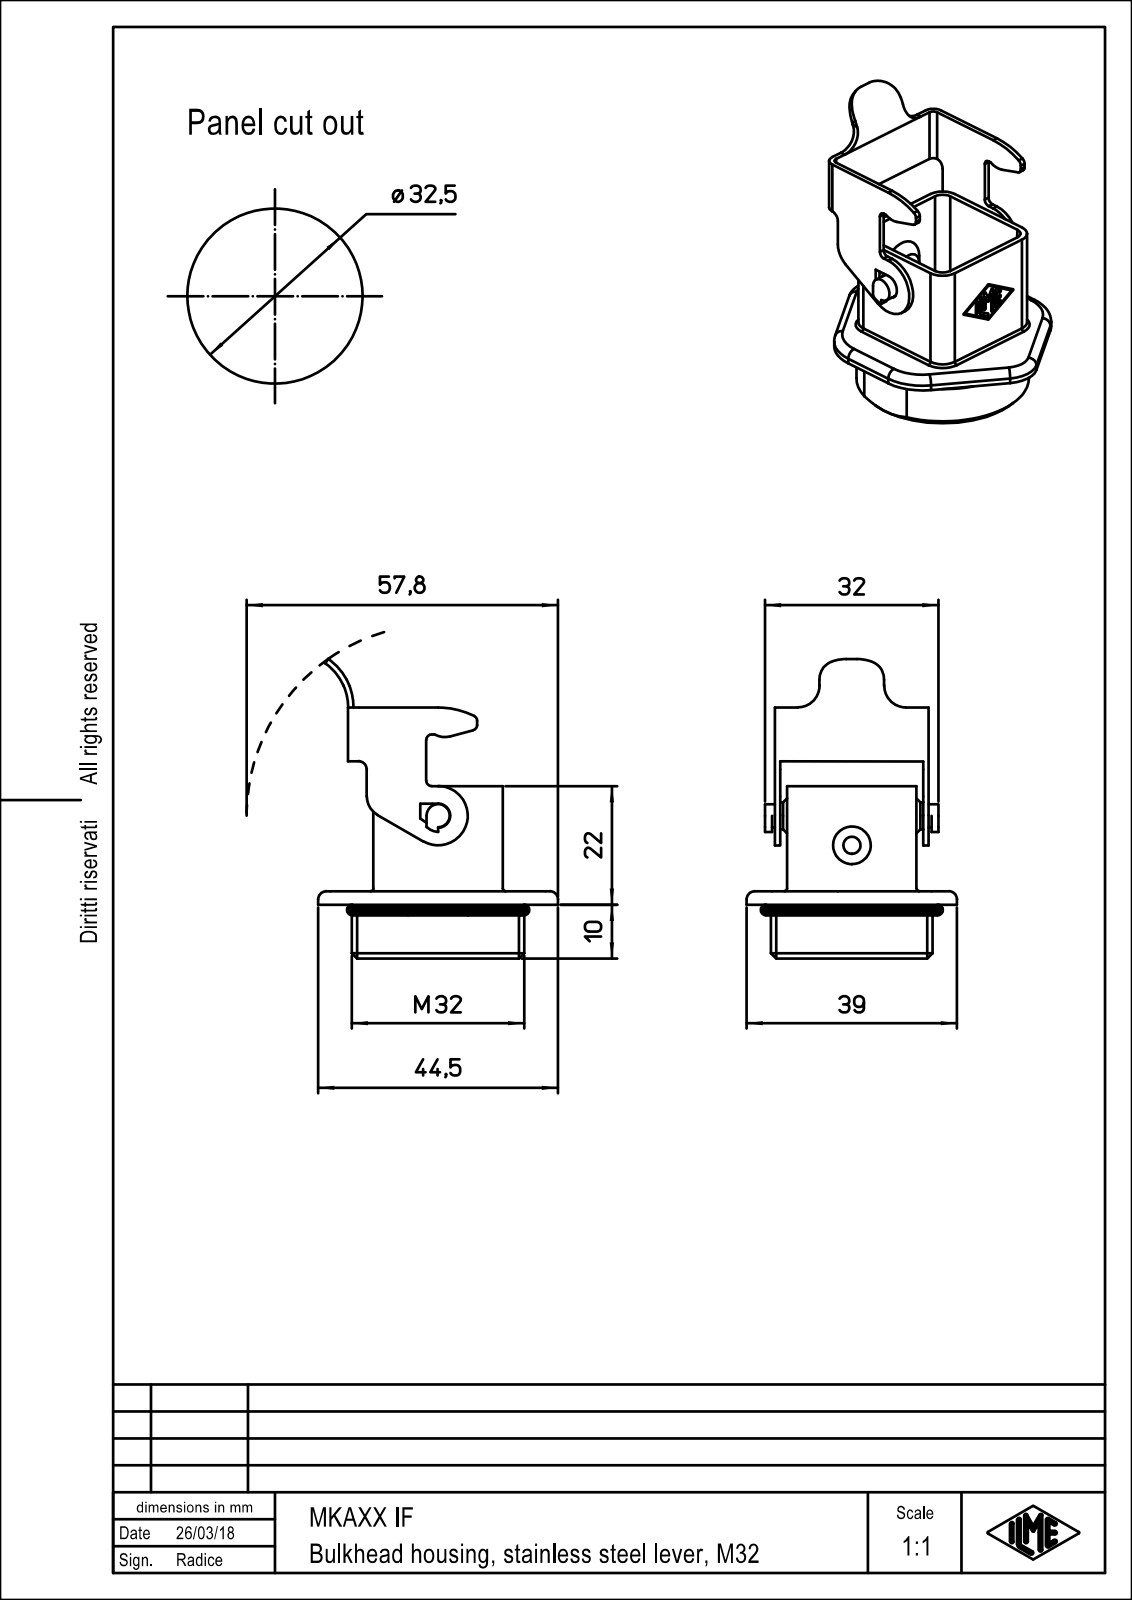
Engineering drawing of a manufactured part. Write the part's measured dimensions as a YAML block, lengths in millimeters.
part_name: "MKAXX_IF"
step_written_by: "PTC Creo Elements/Direct Modeling 19.0E 27-Jun-2016 (C) Parametric Technology GmbH (AUTOMOTIVE_DESIGN)"
units: millimeters
bodies: {solids: 1, faces: 169, planar: 75, cylindrical: 72, other: 22}
overall_size: [55.6, 44.5, 39]
volume: 9261
surface_area: 10675
round_holes:
  - {diameter: 3.2, count: 1}
  - {diameter: 7, count: 1}
round_bosses_or_shafts:
  - {diameter: 29.8, count: 1}
  - {diameter: 5, count: 1}
  - {diameter: 4.3, count: 1}
partial_cylinders:
  - {radius: 1.5, count: 7}
  - {radius: 1, count: 6}
  - {radius: 2, count: 6}
  - {radius: 0.5, count: 4}
  - {radius: 3.2, count: 4}
  - {radius: 4, count: 4}
  - {radius: 9, count: 4}
  - {radius: 5, count: 2}
face_to_face_distances: [1, 27.5, 24, 1.25, 25.25, 2.25, 26.25, 2.5, 28.5, 26.5]
